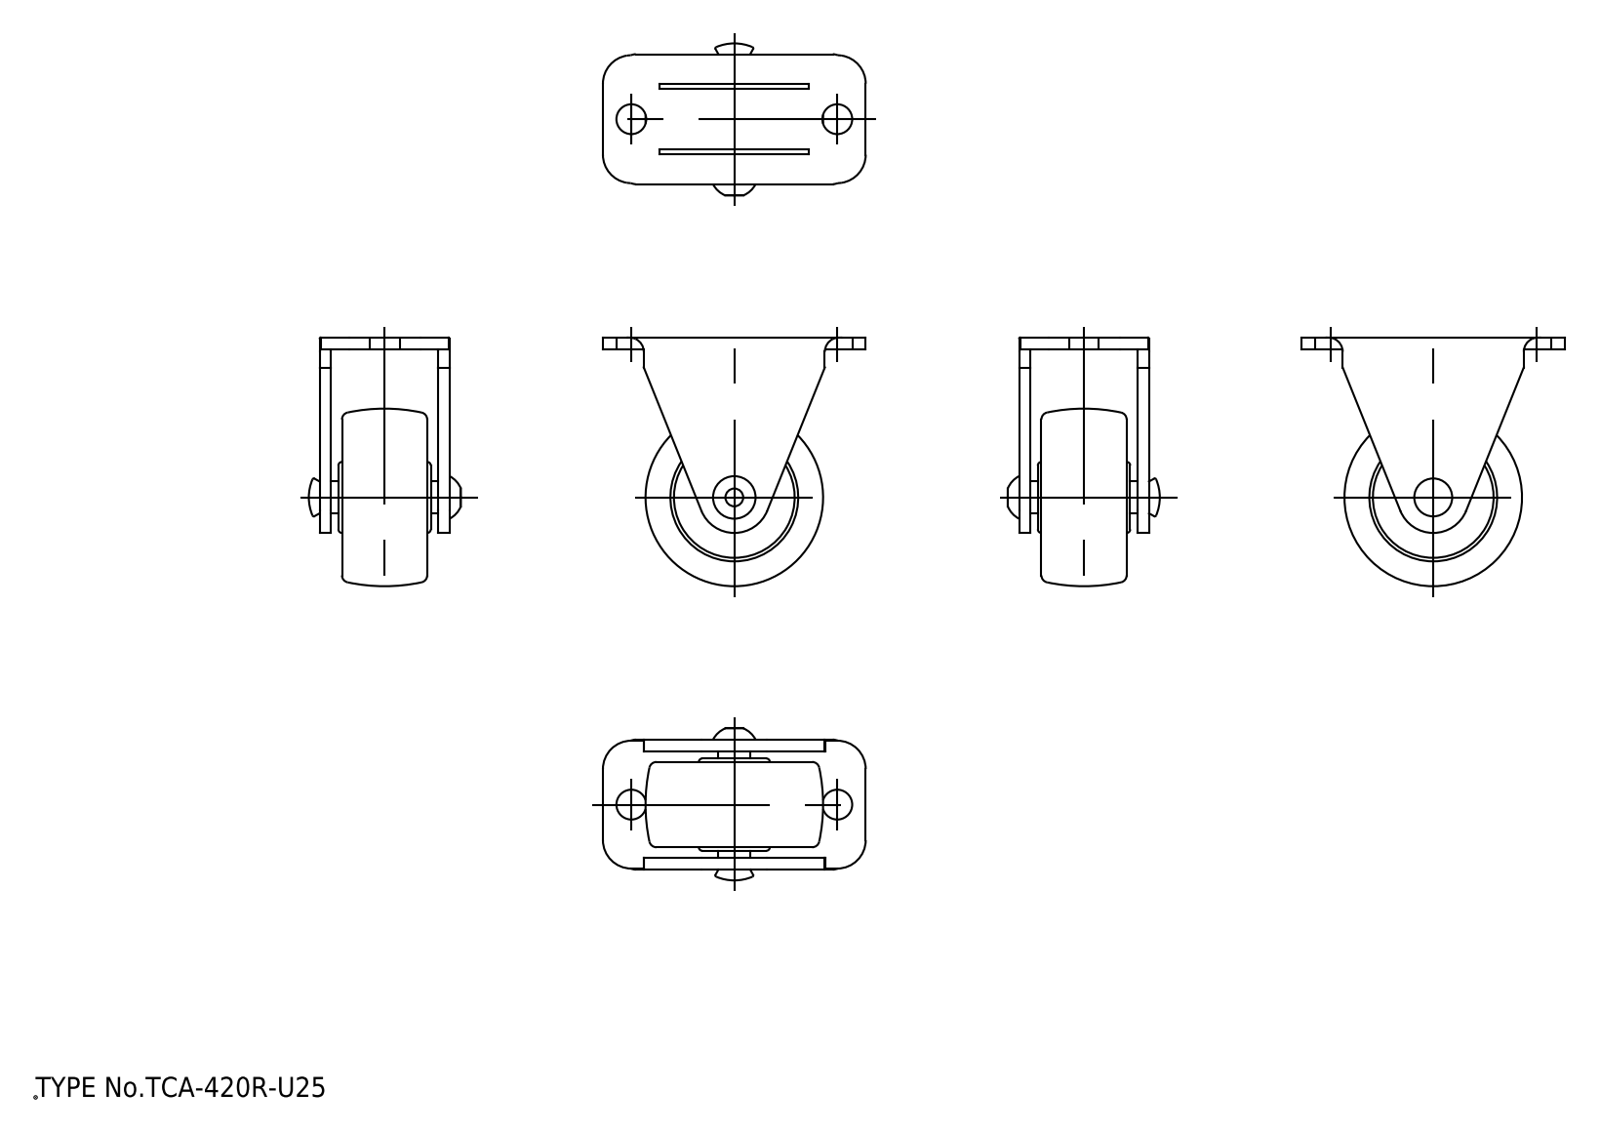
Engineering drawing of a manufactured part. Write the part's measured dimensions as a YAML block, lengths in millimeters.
part_name: "axle; body_new; wheel"
step_written_by: "spGate 19.8.4 (****-****-****-****) (AUTOMOTIVE_DESIGN)"
units: millimeters
bodies: {solids: 3, faces: 89, planar: 37, cylindrical: 28, other: 24}
overall_size: [37, 35, 21.41]
volume: 8053
surface_area: 5659
round_holes:
  - {diameter: 4.2, count: 2}
  - {diameter: 4.5, count: 1}
  - {diameter: 4.7, count: 1}
round_bosses_or_shafts:
  - {diameter: 10, count: 1}
partial_cylinders:
  - {radius: 4, count: 4}
  - {radius: 0.2, count: 2}
  - {radius: 2, count: 2}
face_to_face_distances: [1.6, 16.7, 18.3, 15.1, 0.5, 3.65, 14.65, 2.05, 13.05, 1.55]
hole_center_spacings: [29]
